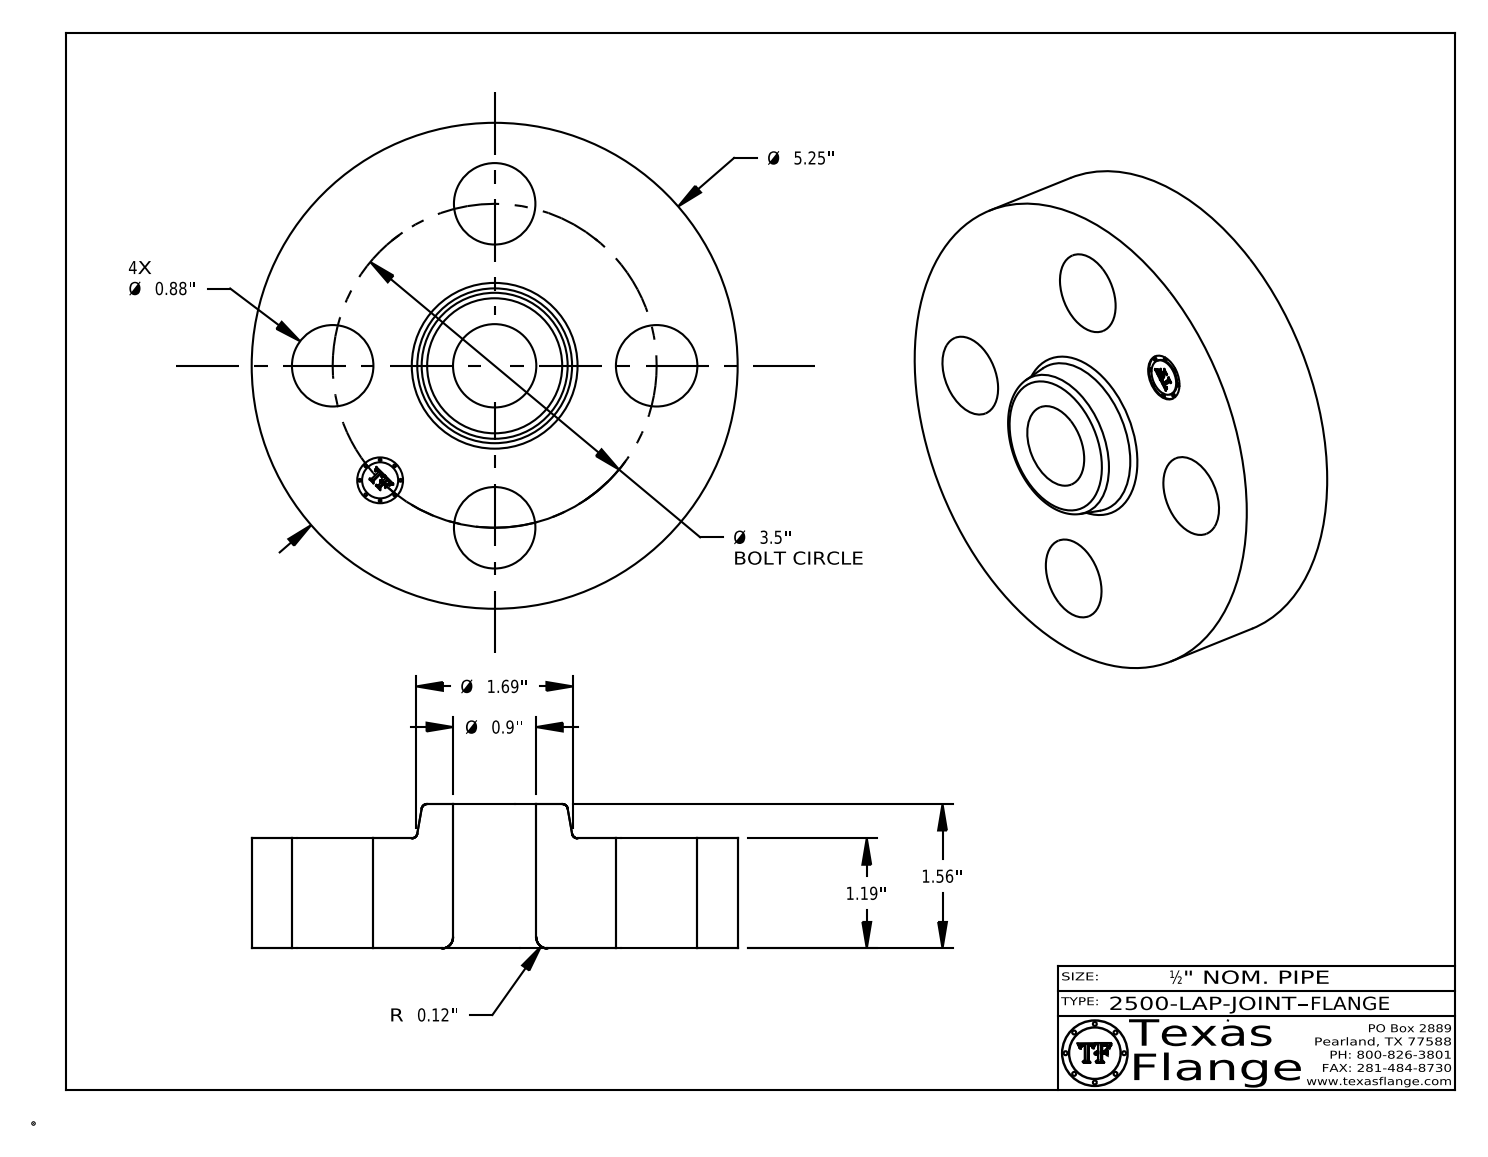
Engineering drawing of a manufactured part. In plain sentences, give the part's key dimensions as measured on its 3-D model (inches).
The part is named "2500-LAP-JOINT FLANGE". Its 3-D file was written by "CATIA V5 STEP AP214 (AUTOMOTIVE_DESIGN)". It is 1 solid with 408 faces: 368 planar, 32 cylindrical and 8 other. Overall it measures 5.25 by 5.25 by 1.56 inches. Its volume is 22.63 cubic inches and its surface area 75.72 square inches. Round holes: 4 of diameter 0.88, 1 of diameter 0.495, 1 of diameter 0.9. Round bosses or shafts: 8 of diameter 0.03, 1 of diameter 5.25, 1 of diameter 0.39. The main face-to-face distances are 1.19, 1.56, 0.37, 1.175, 0.015, 0.385, 0.148, 0.145, 0.027, 0.096. The hole center spacings are 1.75, 2.475, 1.339, 3.233, 3.5.
